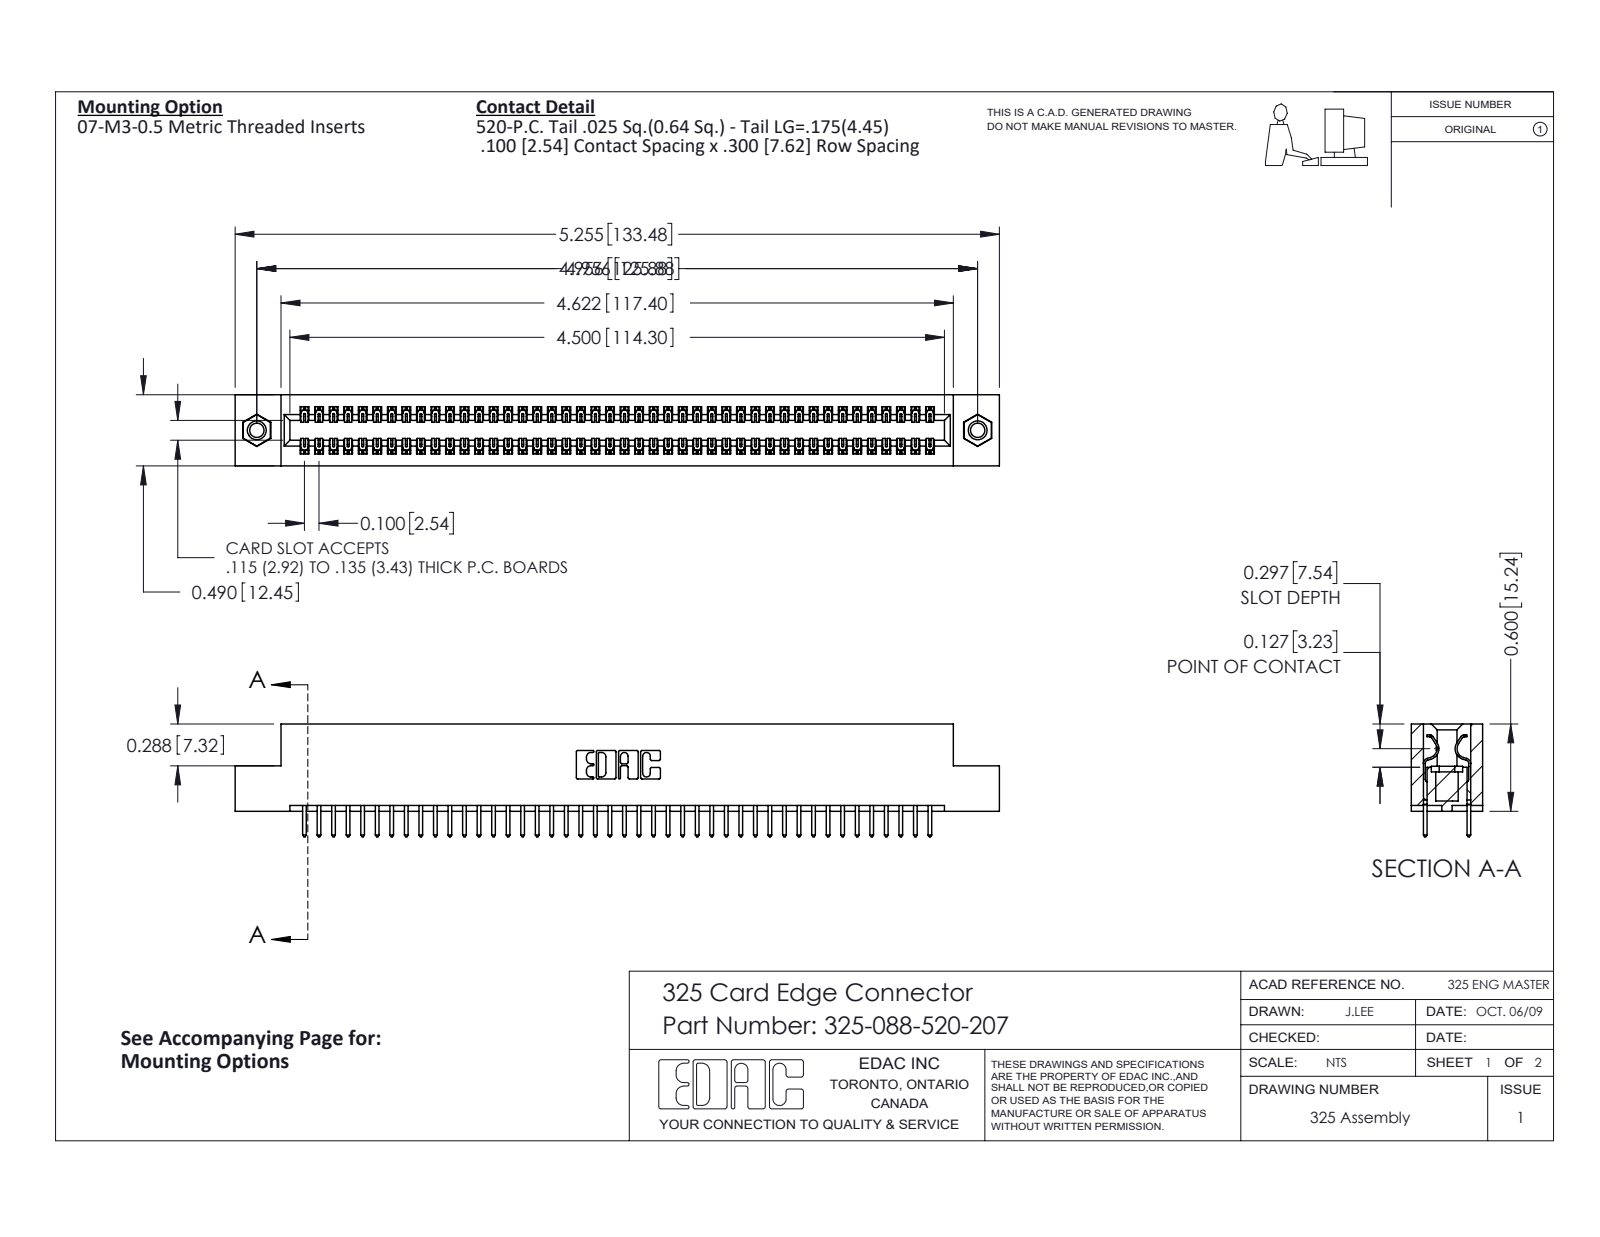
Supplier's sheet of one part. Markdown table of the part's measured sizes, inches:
| quantity | value |
| --- | --- |
| part name | 345-250-001_345-250-005-103; 325-088-520-207; 325 Part_TI; 325-292-001_325-293-120 |
| STEP written by | SolidWorks 2016 (CONFIG_CONTROL_DESIGN) |
| units | inches |
| bodies | 91 solids, 4750 faces (3270 planar, 1464 cylindrical, 16 other) |
| overall size | 5.255 × 0.775 × 0.49 |
| volume | 1.051 in³ |
| surface area | 32.15 in² |
| round holes (diameter × count) | 0.098 × 2, 0.125 × 2, 0.16 × 2 |
| round bosses / shafts (diameter × count) | 0.155 × 2 |
| partial cylindrical surfaces (radius × count) | 0.006 × 132, 0.01 × 88, 0.01 × 22, 0.007 × 6, 0.031 × 6, 0.026 × 3, 0.014 × 2, 0.022 × 2 |
| main face-to-face distances | 0.083, 0.407, 0.3, 0.49, 0.107, 0.383, 0.025, 0.325, 0.275, 0.56 |
| hole center spacings | 4.956 |
